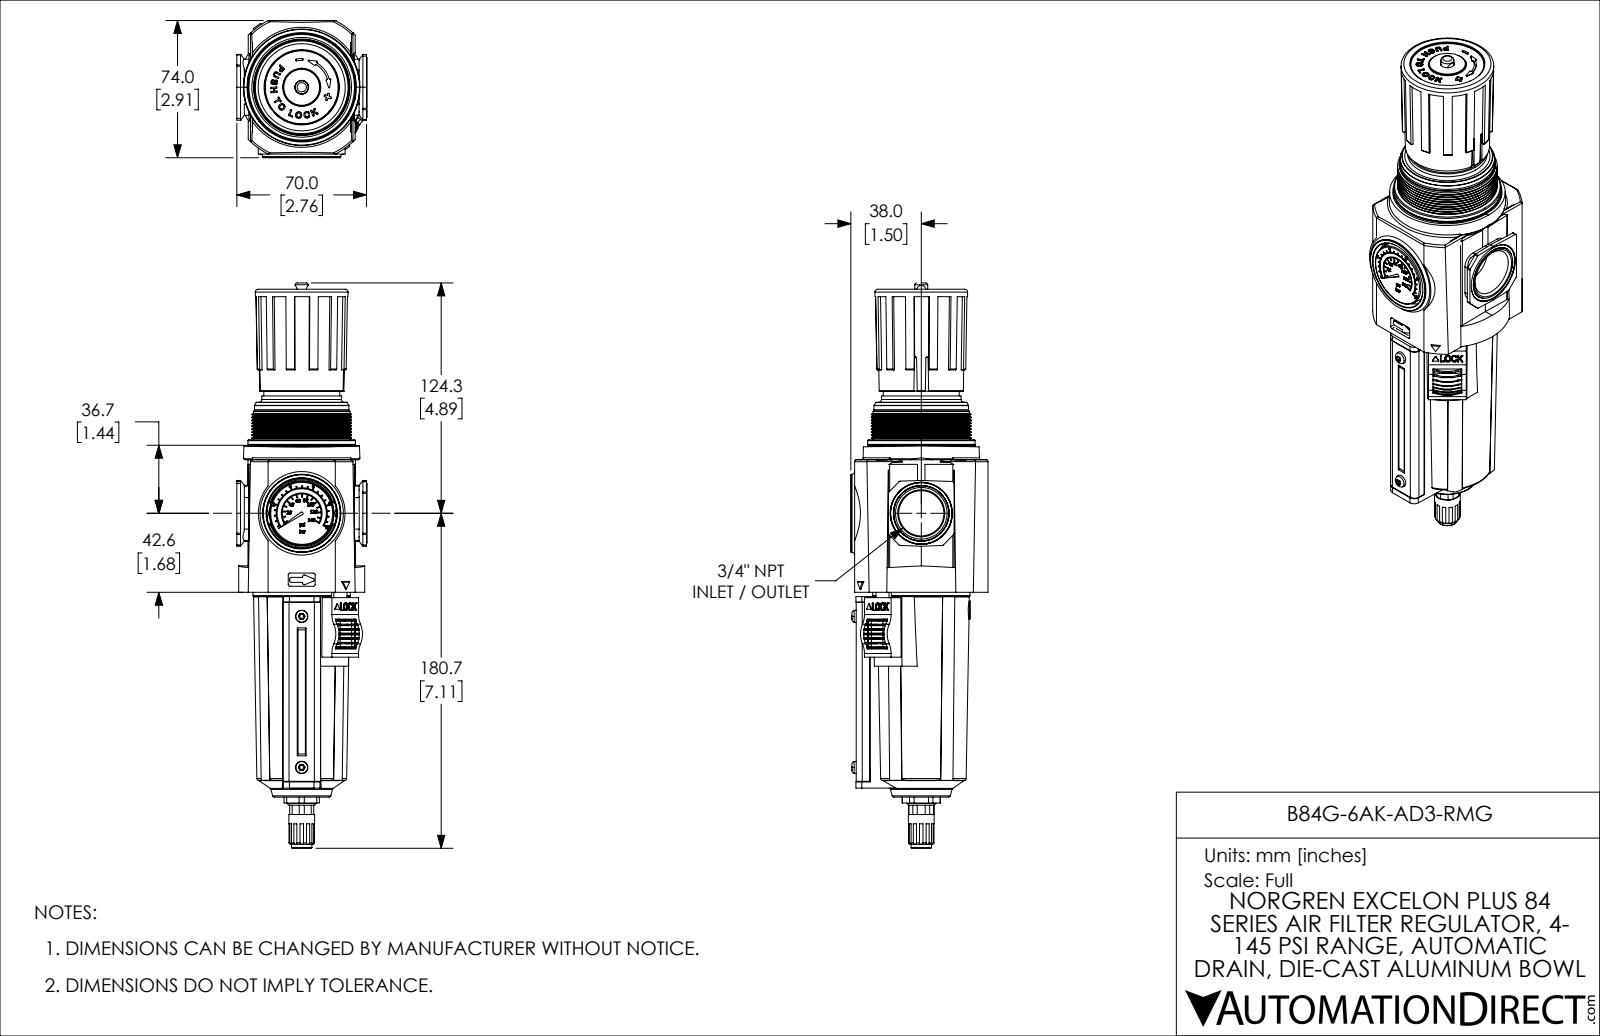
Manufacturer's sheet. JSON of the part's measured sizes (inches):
{"part_name": "B84G-6AK-AD3-RMG", "step_written_by": "SolidWorks 2021 (CONFIG_CONTROL_DESIGN)", "units": "inches", "bodies": {"solids": 9, "faces": 2717, "planar": 1003, "cylindrical": 1241, "other": 473}, "overall_size": [12.005, 2.913, 2.766], "volume_in3": 46.12, "surface_area_in2": 226.5, "round_holes": [[0.112, 2], [0.177, 2], [0.059, 1], [0.197, 1], [0.22, 1], [0.246, 1], [0.633, 1], [0.776, 1], [1.319, 1], [2.323, 1], [2.461, 1]], "round_bosses_or_shafts": [[0.299, 2], [0.213, 2], [0.157, 2], [2.283, 1], [2.122, 1], [2.119, 1], [2.067, 1], [2.047, 1]], "partial_cylinders_radius": [[0.039, 48], [0.028, 28], [0.012, 27], [0.02, 23], [0.01, 18], [0.047, 18], [0.03, 16], [0.004, 14]], "face_to_face_distances": [2.719, 2.323, 2.457, 0.512, 0.364, 2.354, 0.622, 0.134, 2.096, 1.732], "hole_center_spacings": [0.856, 2.685, 5.121, 1.713, 2.504, 2.545, 5.049]}
